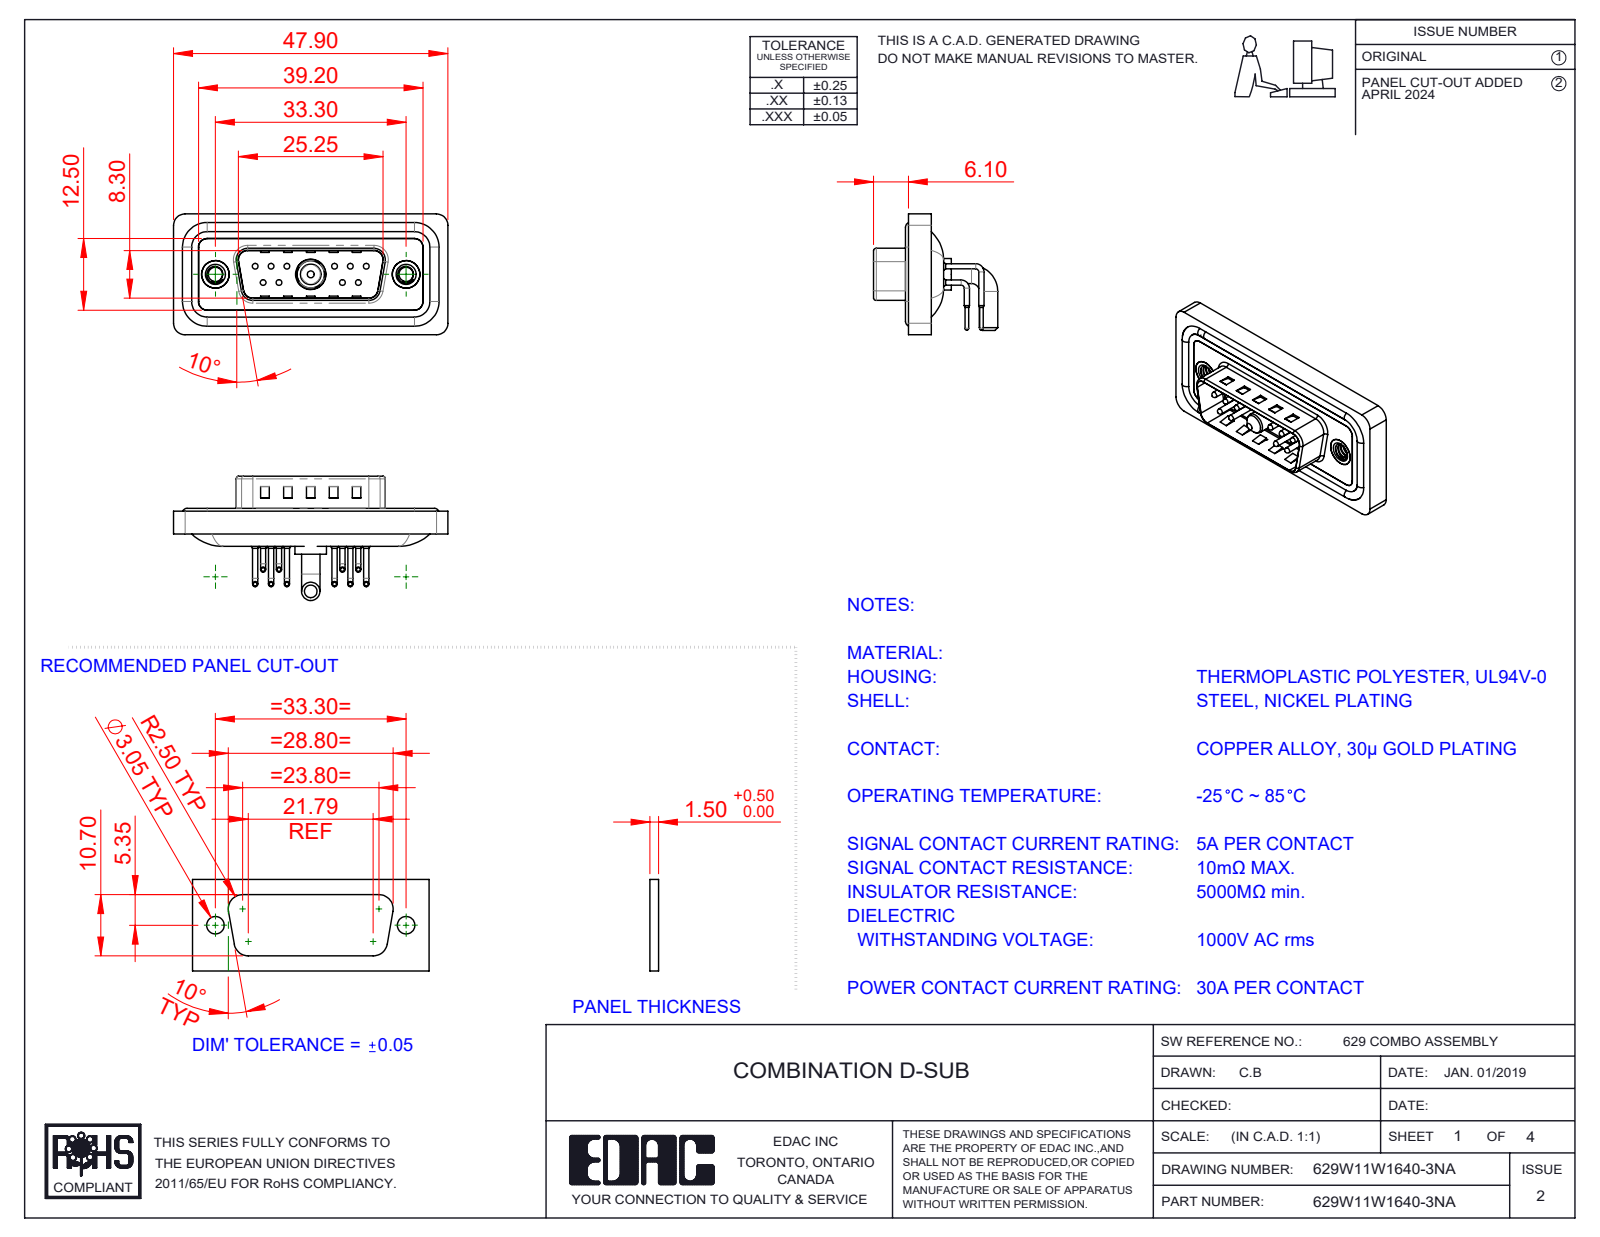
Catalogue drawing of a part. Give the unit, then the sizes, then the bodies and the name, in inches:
Units: inches
Overall size (bounding box): 1.886 × 0.854 × 0.831
Round holes (diameter × count): ⌀0.03 ×10, ⌀0.063 ×10, ⌀0.079 ×10, ⌀0.098 ×2, ⌀0.157 ×2, ⌀0.189 ×2, ⌀0.197 ×2, ⌀0.191 ×1, ⌀0.209 ×1
Round bosses / shafts (diameter × count): ⌀0.035 ×20, ⌀0.059 ×10, ⌀0.039 ×10, ⌀0.026 ×10, ⌀0.063 ×4, ⌀0.193 ×2, ⌀0.126 ×2, ⌀0.217 ×1
Partial cylindrical surfaces — rounded edges, fillets, slot ends (radius × count): R0.079 ×20, R0.059 ×18, R0.04 ×10, R0.02 ×8, R0.063 ×8, R0.039 ×7, R0.01 ×4, R0.024 ×4
Main face-to-face distances: 0.016, 0.114, 0.031, 0.043, 0.083, 0.063, 0.098, 0.161, 0.177, 0.122
Hole centre spacings: 0.124, 0.109, 0.545, 0.436, 0.654, 0.198, 0.198, 0.218
Volume: 0.343 in³ · Surface area: 14.42 in²
Bodies: 19 solids, 1597 faces (836 planar, 567 cylindrical, 194 other)
Part name (STEP PRODUCT): 629W11W1640-3NA; 629Combo Contact Row 1; 629Combo Waterproof Housing_15 Contacts; 629Combo Shell Rear_15 Contacts (+5 more)
STEP written by: SolidWorks 2023 (CONFIG_CONTROL_DESIGN)
